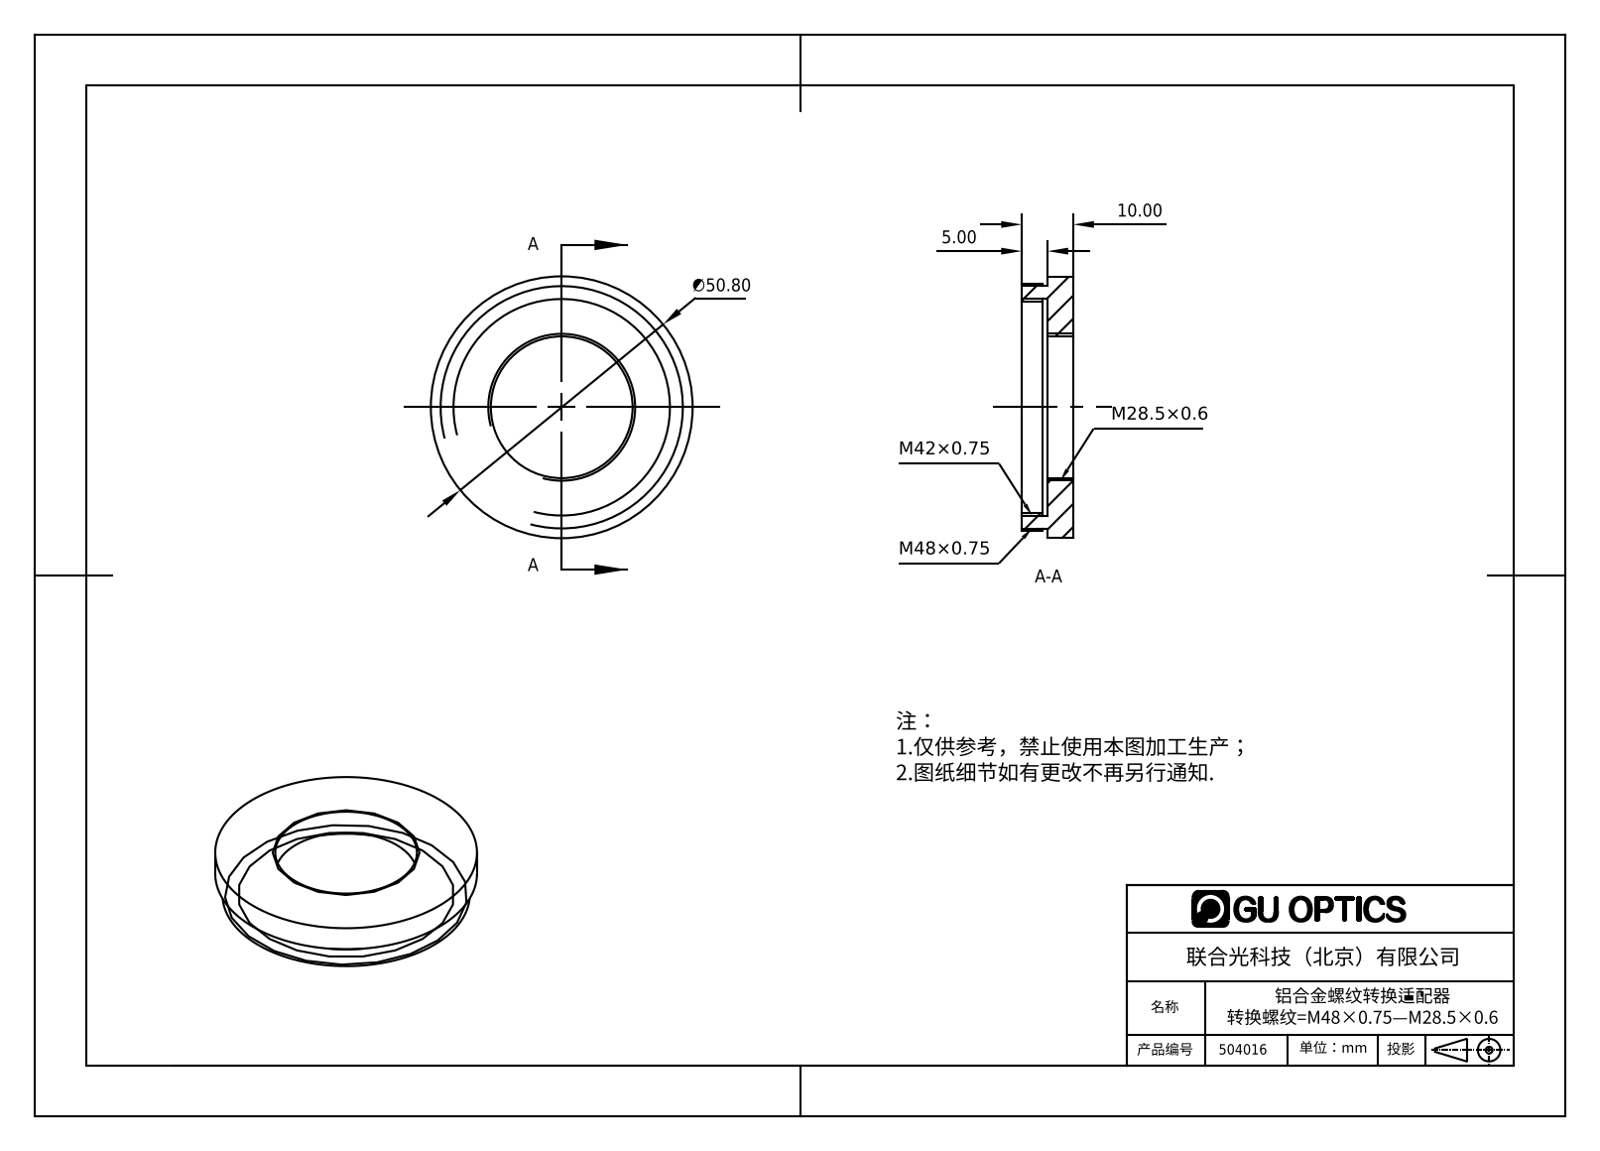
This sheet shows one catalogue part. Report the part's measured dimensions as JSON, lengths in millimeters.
{"part_name": "504016", "step_written_by": "SolidWorks 2016 (AUTOMOTIVE_DESIGN)", "units": "millimeters", "bodies": {"solids": 1, "faces": 18, "planar": 6, "cylindrical": 12, "other": 0}, "overall_size": [50.8, 50.8, 10], "volume_mm3": 9458, "surface_area_mm2": 5800, "round_holes": [[27.5, 1], [41, 1], [42.2, 1]], "round_bosses_or_shafts": [[50.8, 1], [48, 1], [47, 1]], "face_to_face_distances": [5, 10, 4, 1, 6]}
